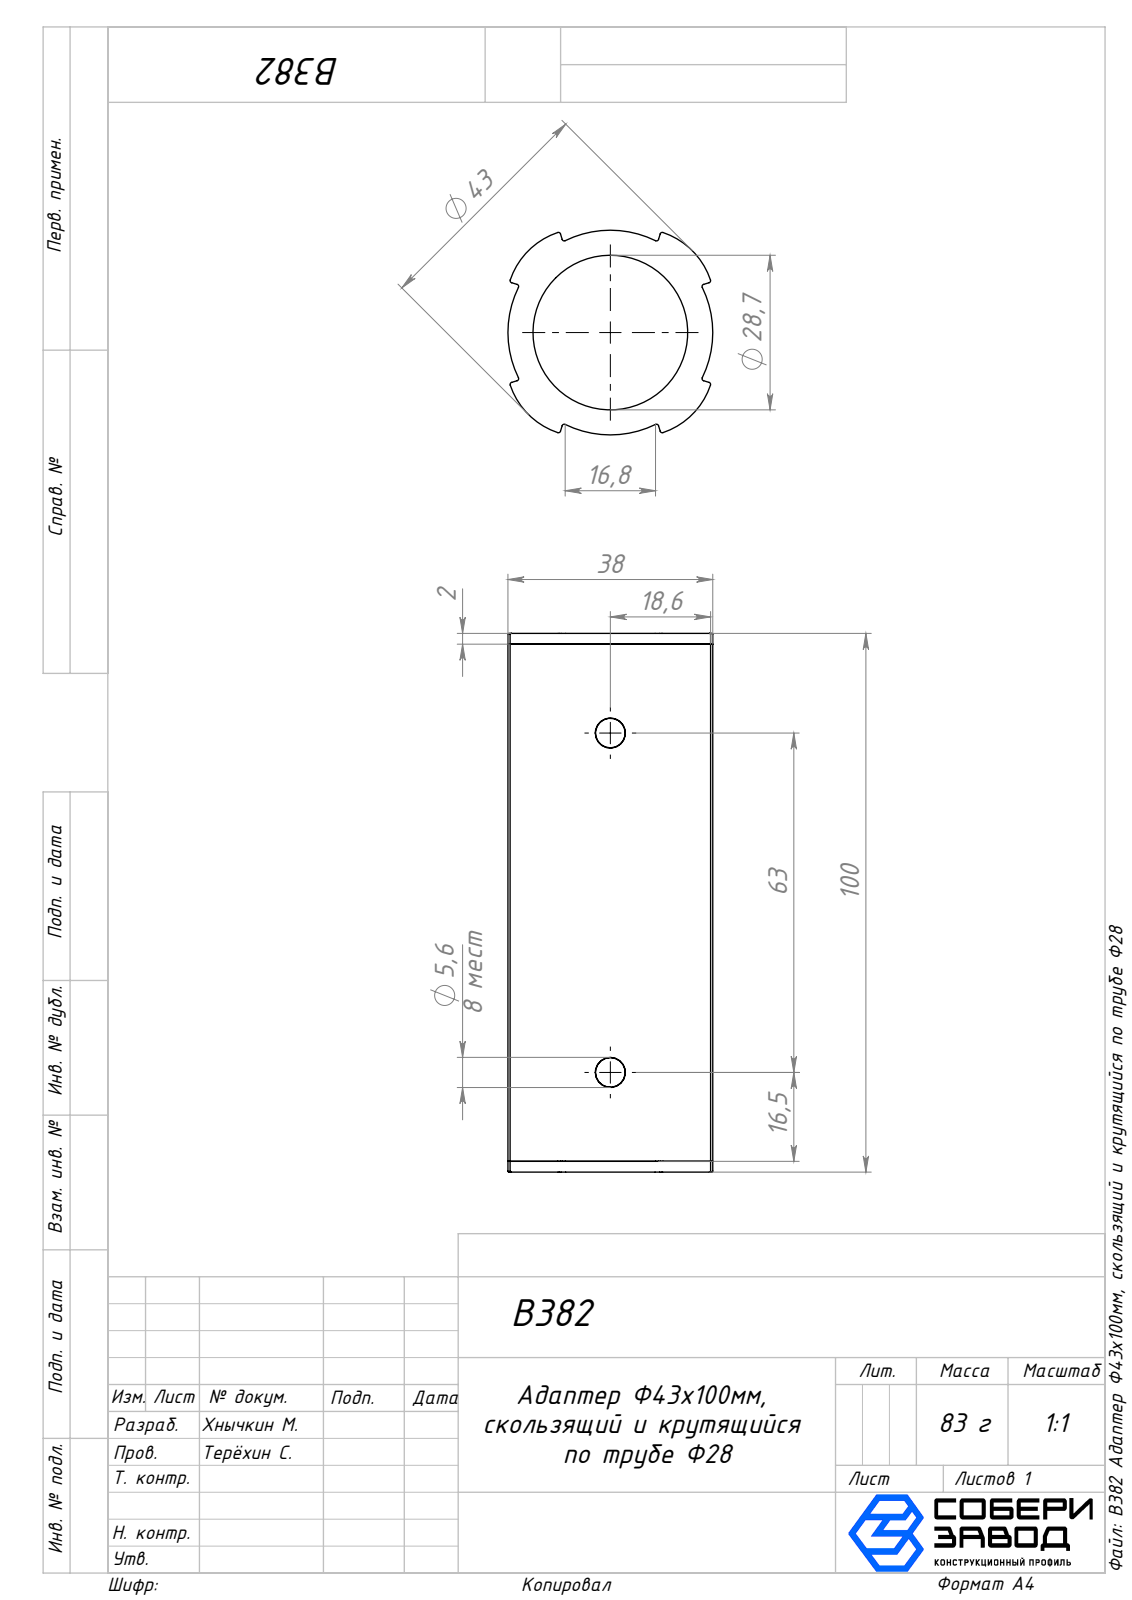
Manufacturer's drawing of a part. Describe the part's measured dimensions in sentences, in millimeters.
The part is named "B382 Адаптер Ф43х100мм, скользящий и крутящийся по трубе Ф28; Крышка_00; Корпус_00". Its 3-D file was written by "SolidWorks 2025 (AUTOMOTIVE_DESIGN)". It is 3 solids with 386 faces: 96 planar, 208 cylindrical and 82 other. Overall it measures 100 by 38 by 38 millimeters. Its volume is 33 607 cubic millimeters and its surface area 34 375 square millimeters. Round holes: 2 of diameter 5.6, 1 of diameter 28.7, 1 of diameter 30. Round bosses or shafts: 1 of diameter 33.6. Partial cylindrical surfaces (rounded edges, fillets, slot ends): 20 of radius 0.5, 16 of radius 0.2, 16 of radius 0.4, 12 of radius 1, 4 of radius 14, 2 of radius 16.8, 1 of radius 17, 1 of radius 19. The main face-to-face distances are 2, 98, 20.59, 96, 100, 7.08, 9.5, 13, 87, 11. The hole center spacings are 63.
